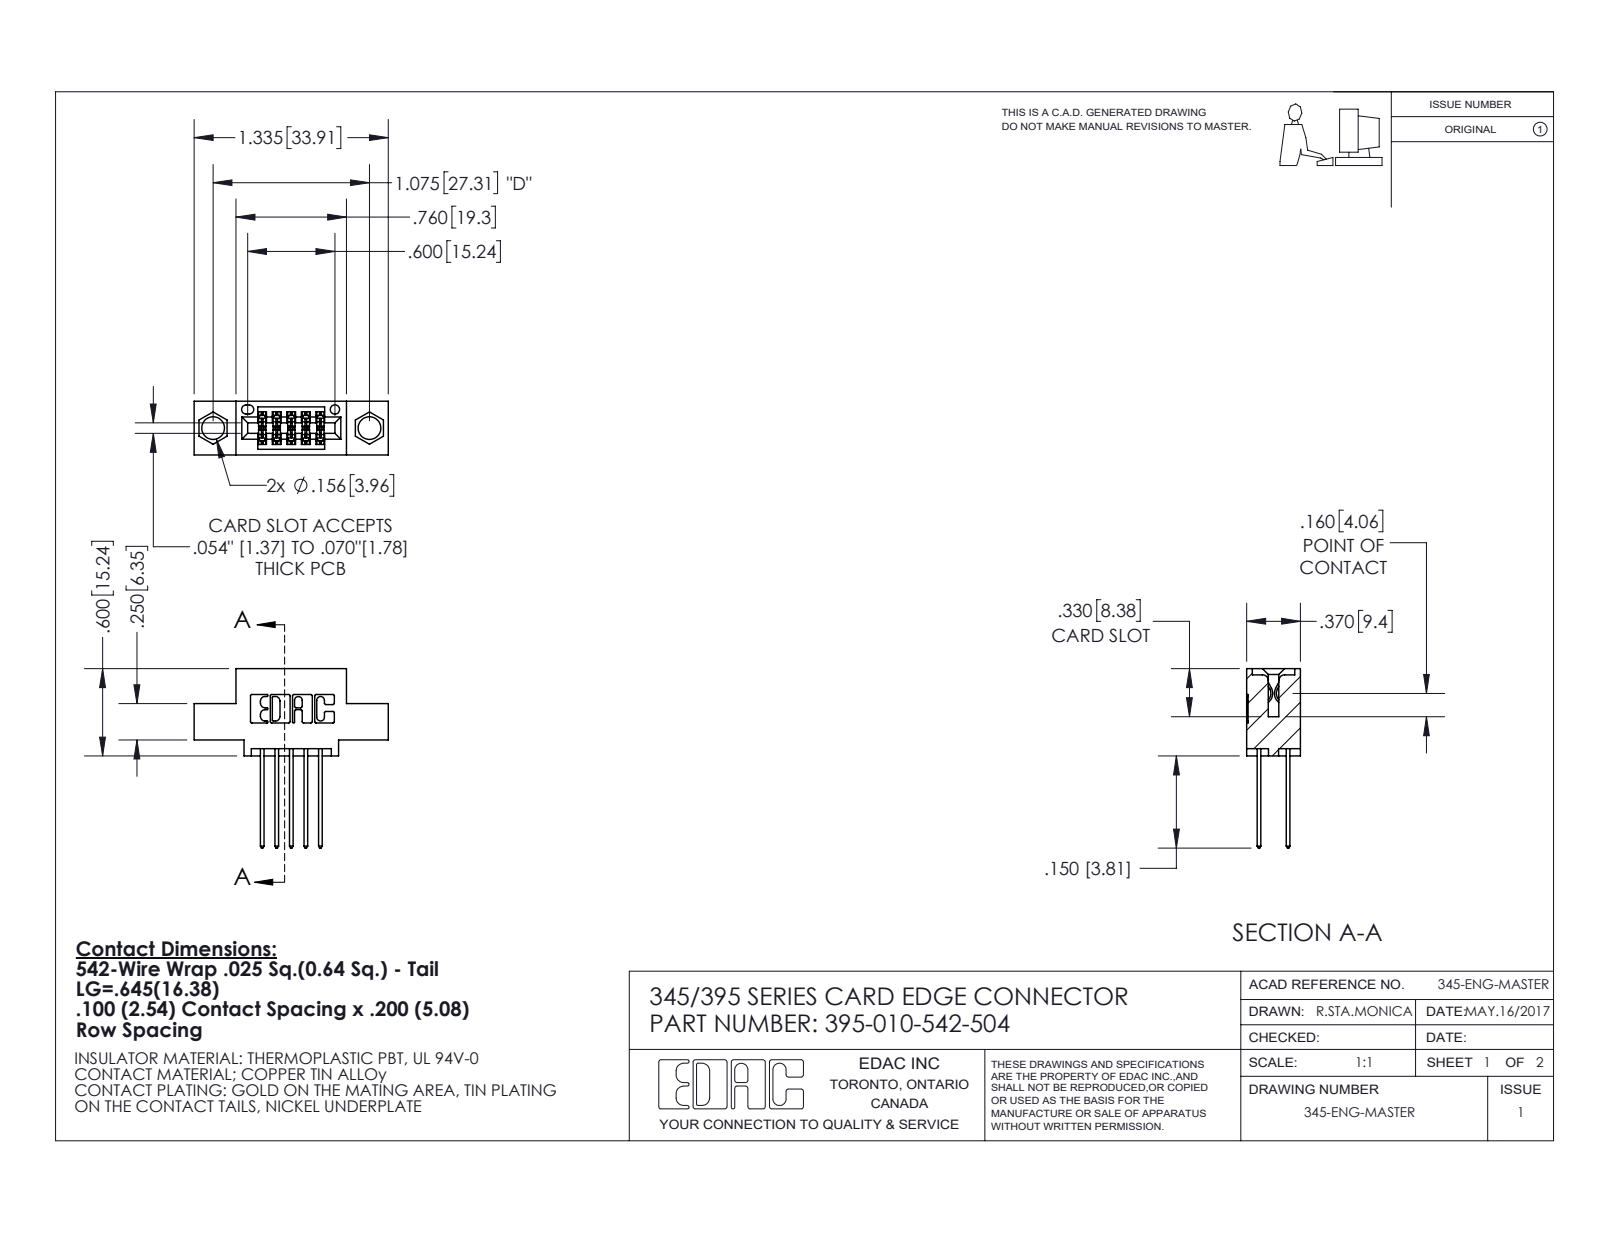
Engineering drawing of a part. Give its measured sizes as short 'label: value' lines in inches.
name: 345-292-001_345-293-142; 345 Part_0.110 Offset - 0.156 Dia-TI; 395-010-542-504
written by: SolidWorks 2020 (CONFIG_CONTROL_DESIGN)
unit: in
bodies: 11 solids, 644 faces (428 planar, 216 cylindrical, 0 other)
size: 1.335 × 1.232 × 0.37
volume: 0.172 in³; area: 5.597 in²
holes: 2× ⌀0.156, 1× ⌀0.064
rounds: 22× R0.01, 15× R0.006, 10× R0.01, 6× R0.007, 6× R0.031, 3× R0.026, 2× R0.014, 2× R0.019
face distances: 0.2, 0.072, 0.298, 0.37, 0.1, 0.098, 0.272, 0.025, 0.225, 0.25
hole spacings: 0.27, 0.847, 1.075
